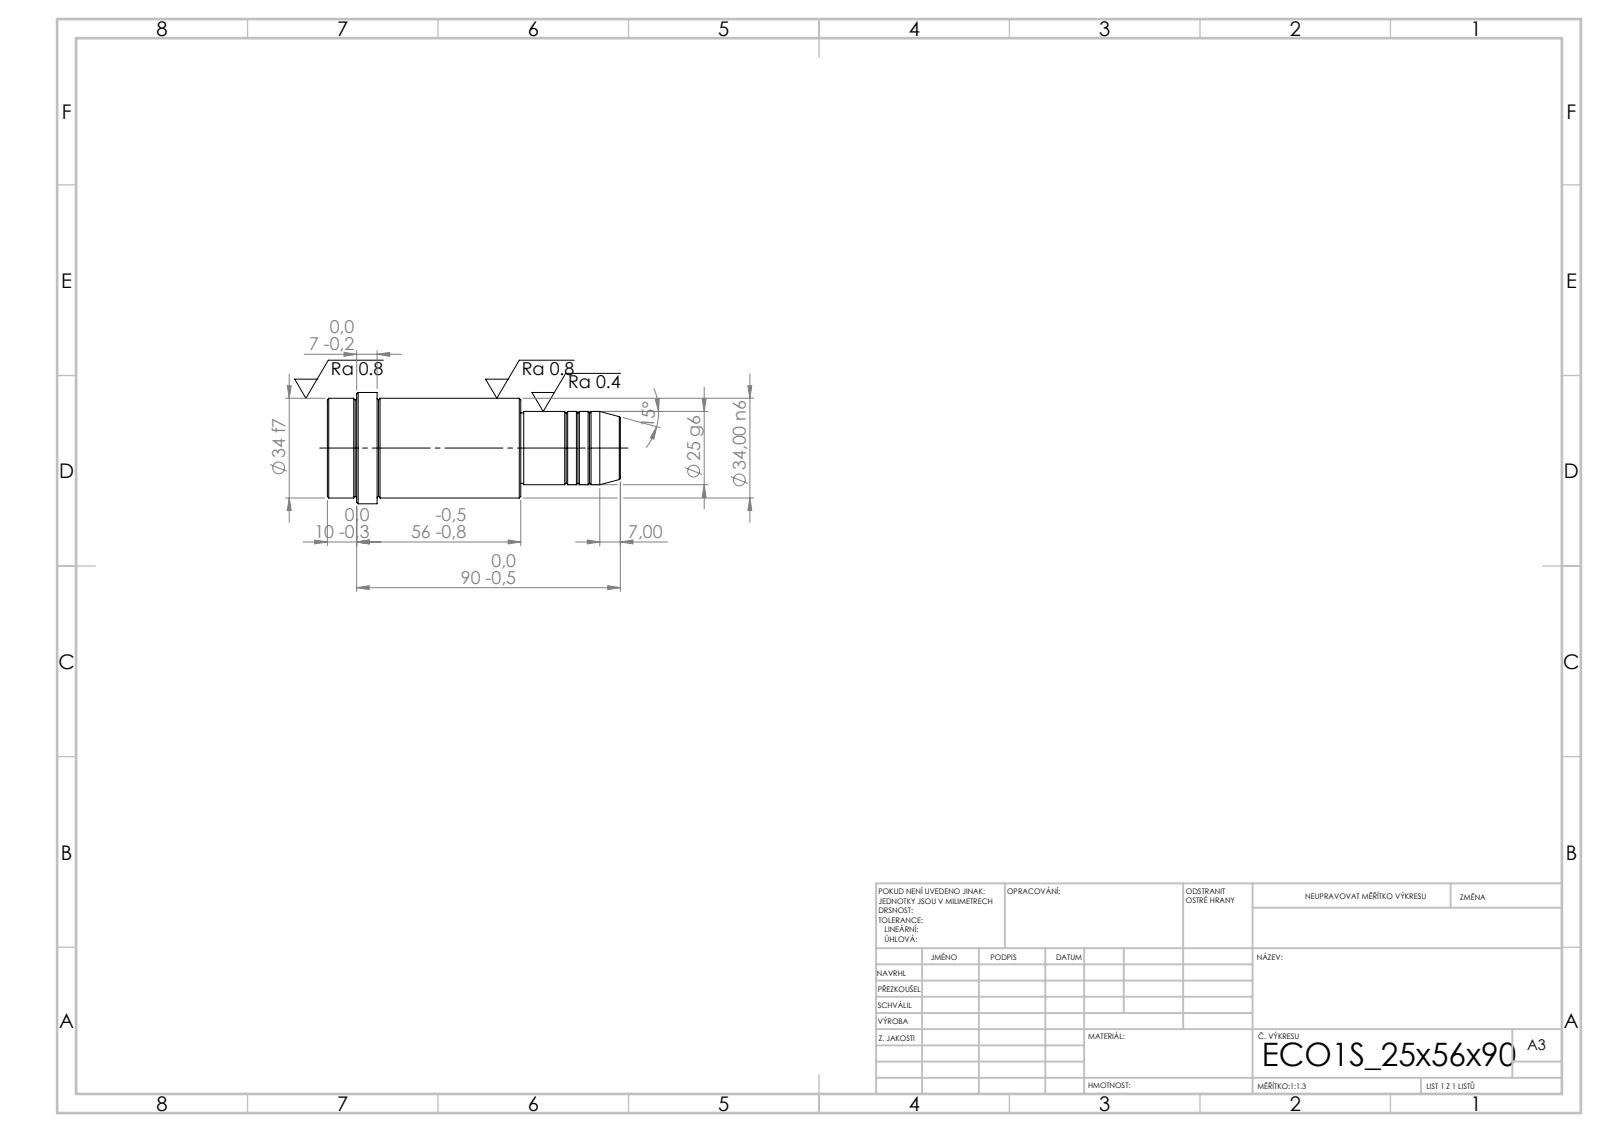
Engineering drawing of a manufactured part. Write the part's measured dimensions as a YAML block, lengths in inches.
step_written_by: "SolidWorks 2019 (CONFIG_CONTROL_DESIGN)"
units: inches
bodies: {solids: 1, faces: 52, planar: 6, cylindrical: 16, other: 30}
overall_size: [3.937, 1.496, 1.496]
volume: 4.726
surface_area: 18.79
round_bosses_or_shafts:
  - {diameter: 1.496, count: 1}
  - {diameter: 1.339, count: 1}
  - {diameter: 0.984, count: 1}
  - {diameter: 0.945, count: 1}
face_to_face_distances: [2.598, 1.339, 3.937, 3.268, 1.929, 0.669, 3.543, 2.205, 0.276, 0.394]
